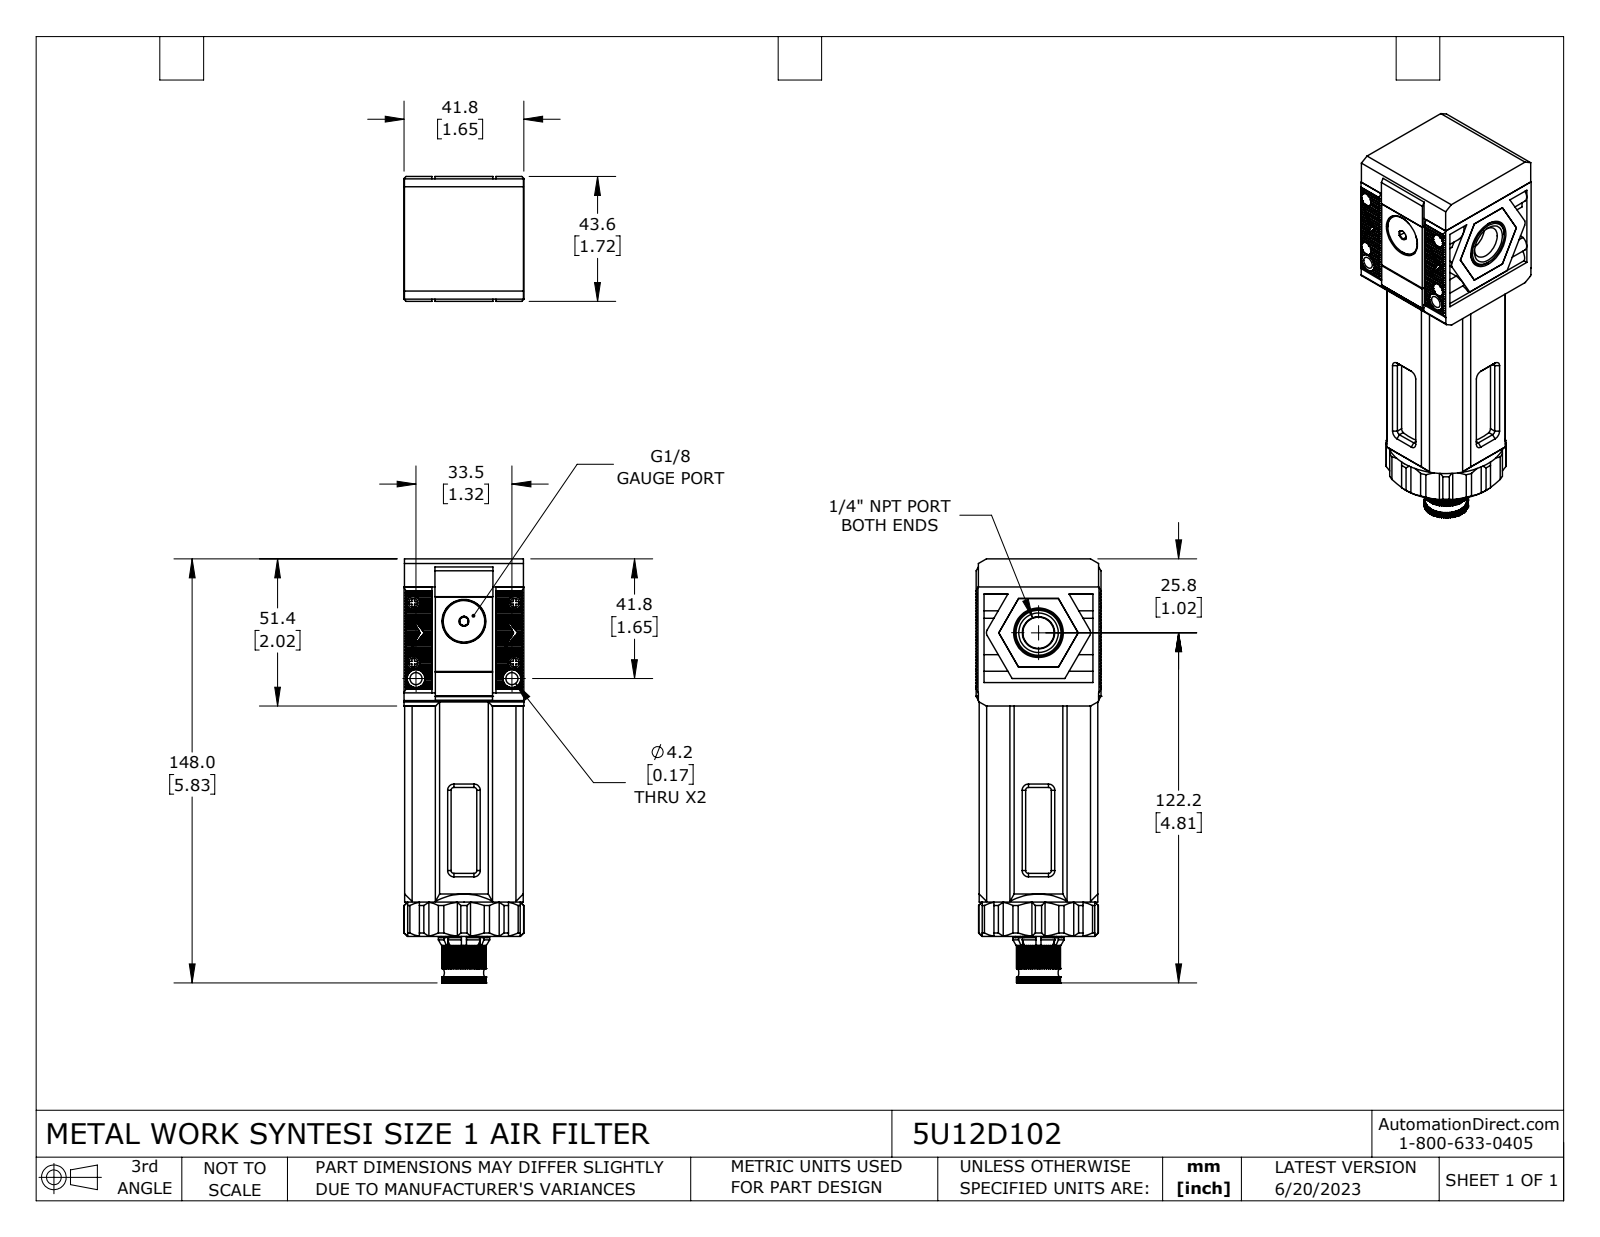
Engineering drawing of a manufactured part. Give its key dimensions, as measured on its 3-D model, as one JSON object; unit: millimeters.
{"part_name": "5U12D102", "step_written_by": "SolidWorks 2021 (CONFIG_CONTROL_DESIGN)", "units": "millimeters", "bodies": {"solids": 14, "faces": 1872, "planar": 1424, "cylindrical": 286, "other": 162}, "overall_size": [148, 43.6, 41.8], "volume_mm3": 130800, "surface_area_mm2": 65350, "round_holes": [[2.1, 4], [3, 4], [4.7, 4], [4.2, 2], [3.2, 1], [7, 1], [8.6, 1], [8.7, 1], [15.3, 1], [30, 1], [34, 1], [35.4, 1]], "round_bosses_or_shafts": [[4.6, 4], [2.6, 4], [6.2, 2], [41.4, 1], [35.6, 1], [25, 1], [22.8, 1], [18.2, 1]], "partial_cylinders_radius": [[1, 8], [0.6, 4], [3.1, 4], [0.2, 2], [2, 2], [7, 1], [7.1, 1], [9, 1]], "face_to_face_distances": [41.6, 41.4, 1.1, 42.5, 9.8, 33.8, 41.7, 7.8, 40, 1.7], "hole_center_spacings": [5.6, 18.8, 20.9, 22.9, 26.1, 26.5, 34.9, 35.4]}
